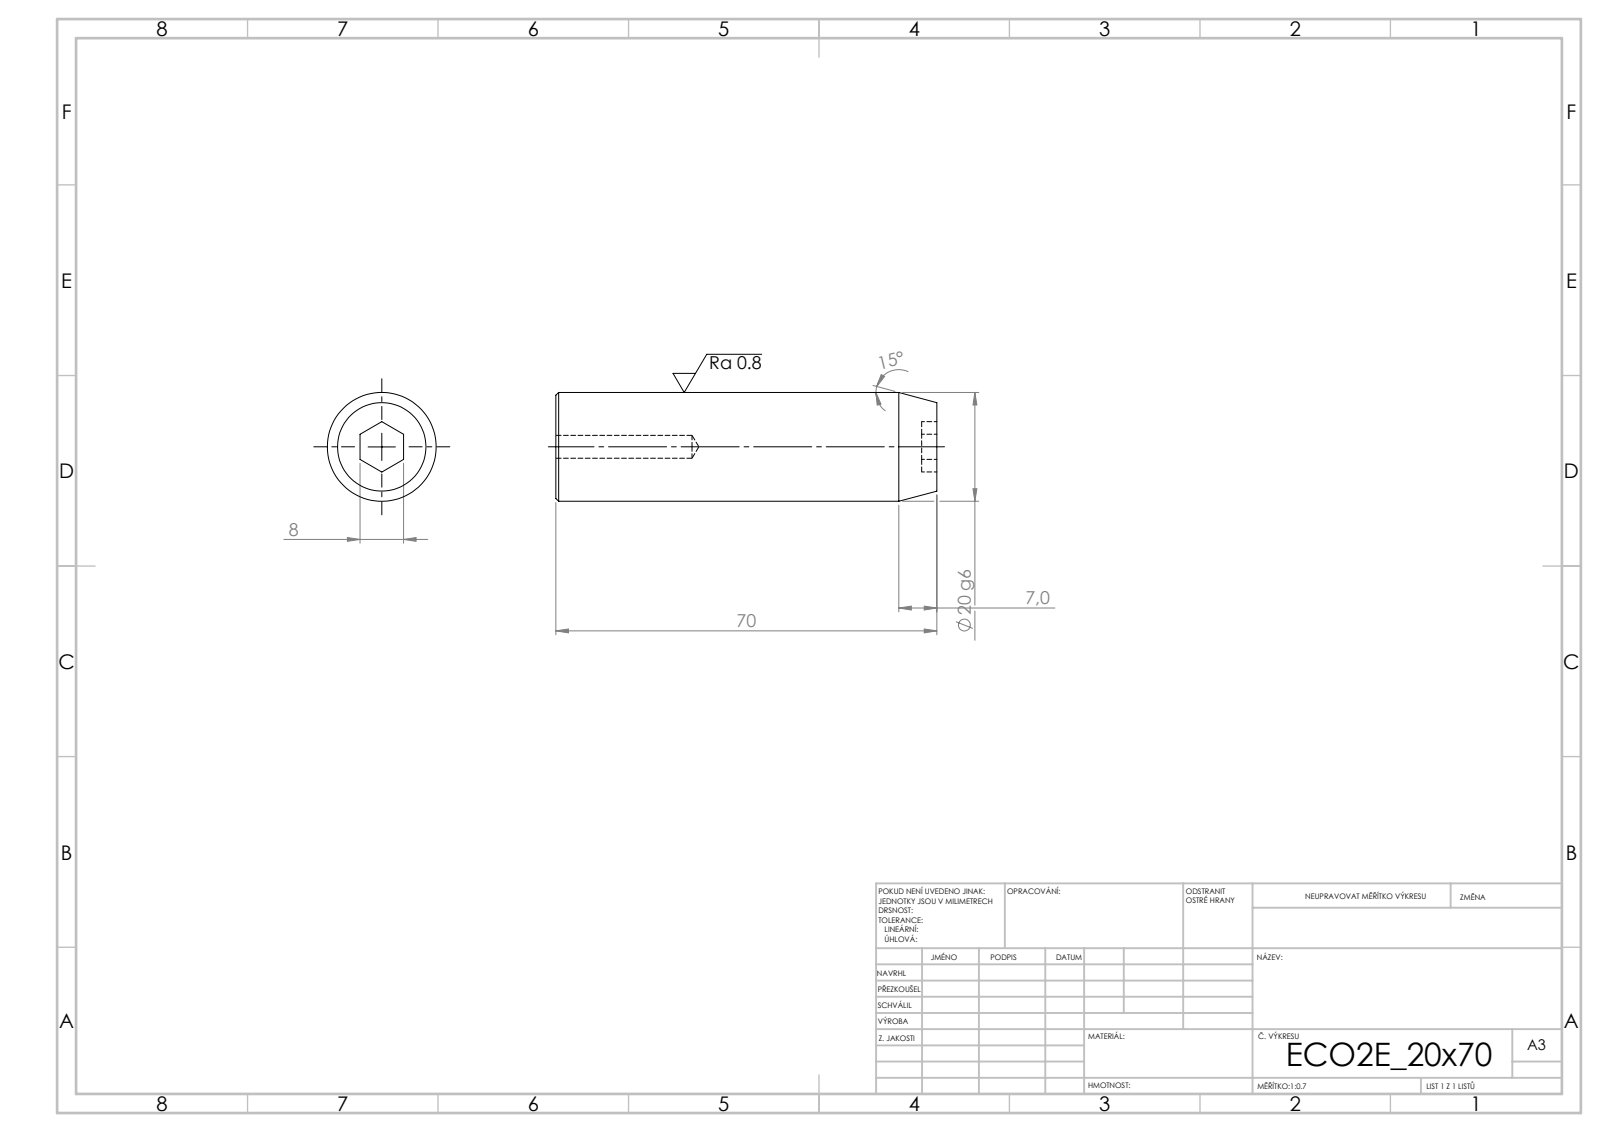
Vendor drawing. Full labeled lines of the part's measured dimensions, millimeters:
STEP written by: SolidWorks 2019 (CONFIG_CONTROL_DESIGN)
Units: millimetres
Bodies: 1 solid, 19 faces (9 planar, 4 cylindrical, 6 other)
Overall size (bounding box): 70 × 20 × 20
Volume: 21 089 mm³ · Surface area: 5 284 mm²
Round holes (diameter × count): ⌀4.2 ×1
Round bosses / shafts (diameter × count): ⌀20 ×1
Main face-to-face distances: 70, 2.8, 67.2, 8
